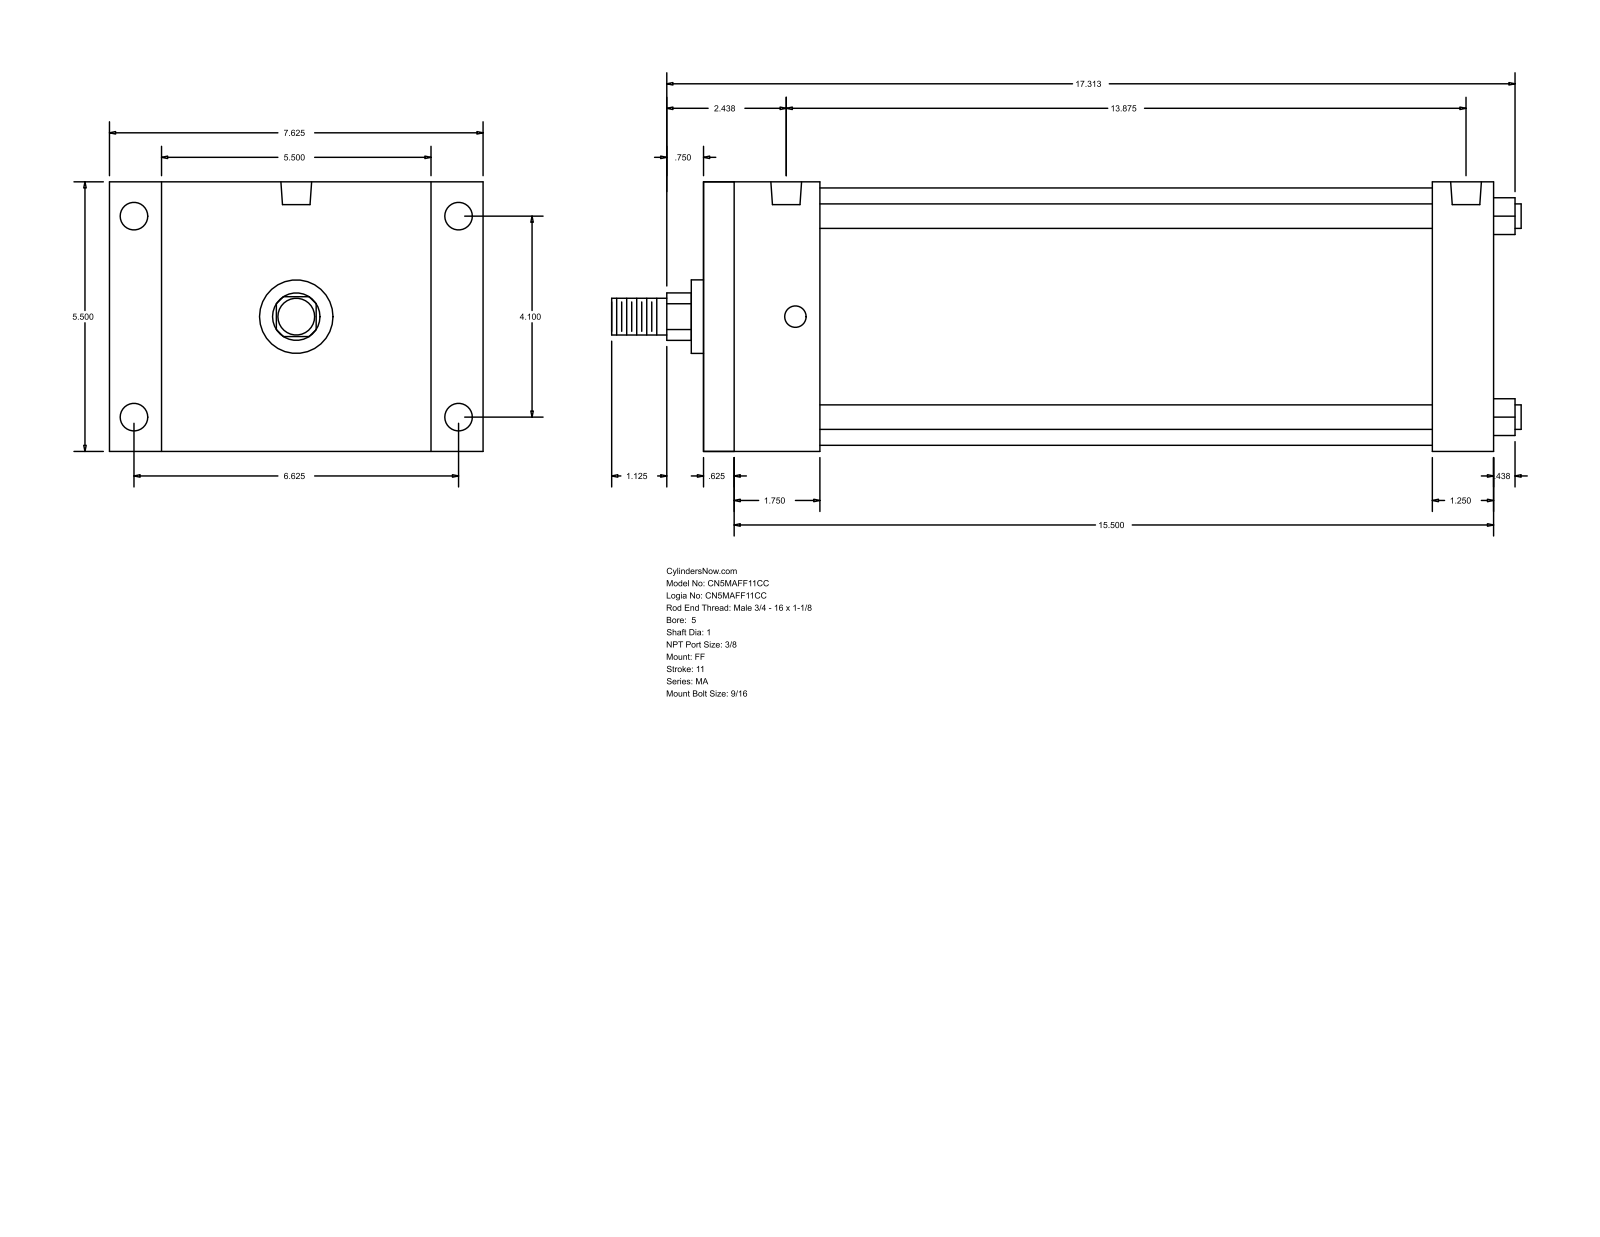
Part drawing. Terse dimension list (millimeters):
name: MA_FF__0500_1
written by: GSSL Pune (CONFIG_CONTROL_DESIGN)
unit: mm
bodies: 0 solids, 92 faces (64 planar, 28 cylindrical, 0 other)
size: 471.49 × 193.68 × 139.7
holes: 4× ⌀11.11, 4× ⌀14.29, 2× ⌀15.93
bosses: 4× ⌀12.7, 1× ⌀133.35, 1× ⌀38.1, 1× ⌀25.4, 1× ⌀19.05
rounds: 1× R12.29
face distances: 139.7, 409.57, 15.87, 393.7, 377.83, 361.96, 31.74, 60.33, 44.46, 317.5
hole spacings: 104.14, 168.28, 197.9, 342.9, 4.76, 4.77, 347.66, 347.67
